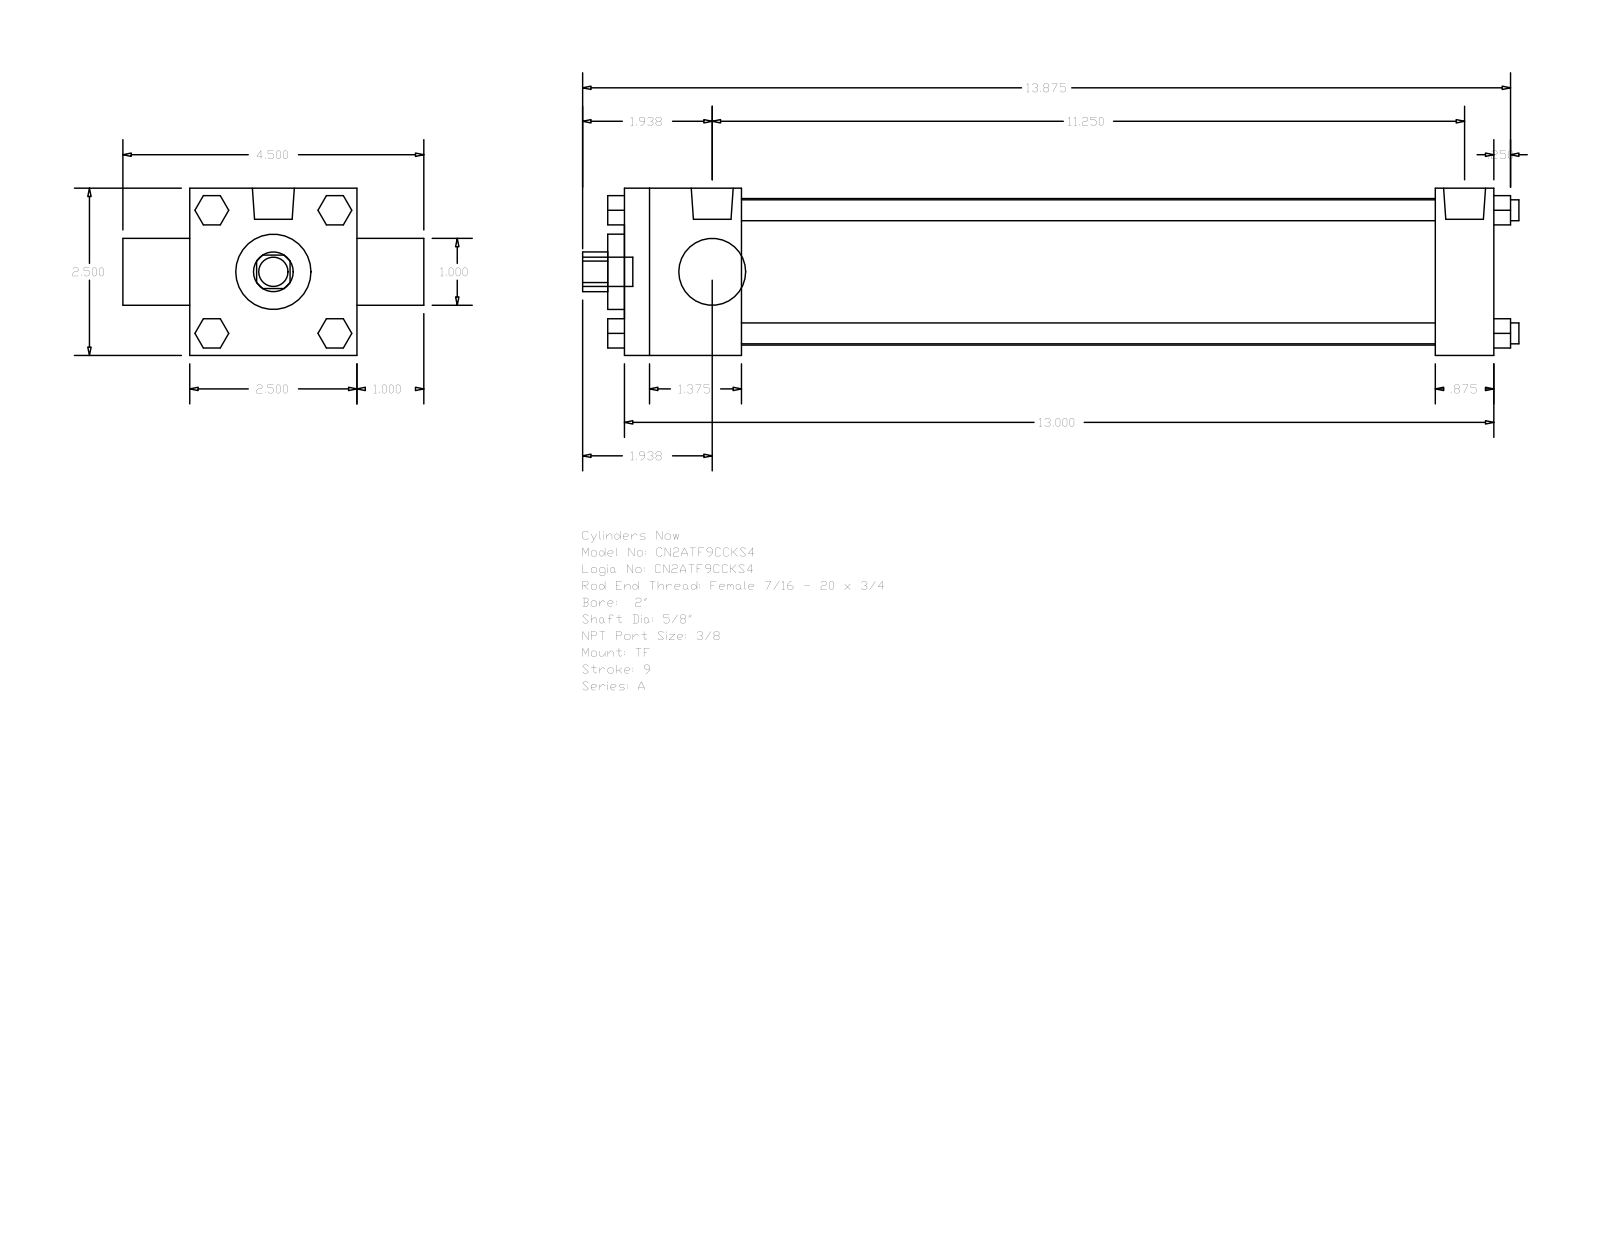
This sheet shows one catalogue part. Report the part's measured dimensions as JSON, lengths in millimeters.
{"part_name": "A_TF__0200_0.625", "step_written_by": "GSSL Pune (CONFIG_CONTROL_DESIGN)", "units": "millimeters", "bodies": {"solids": 0, "faces": 120, "planar": 92, "cylindrical": 28, "other": 0}, "overall_size": [355.6, 114.3, 63.5], "round_holes": [[15.88, 1], [25.4, 1], [28.57, 1], [55.63, 1]], "round_bosses_or_shafts": [[7.94, 4], [5.56, 3], [15.93, 2], [11.11, 1]], "partial_cylinders_radius": [[7.54, 1]], "face_to_face_distances": [63.5, 330.19, 44.45, 307.97, 263.52, 285.74, 22.22, 25.4, 88.9, 50.8]}
